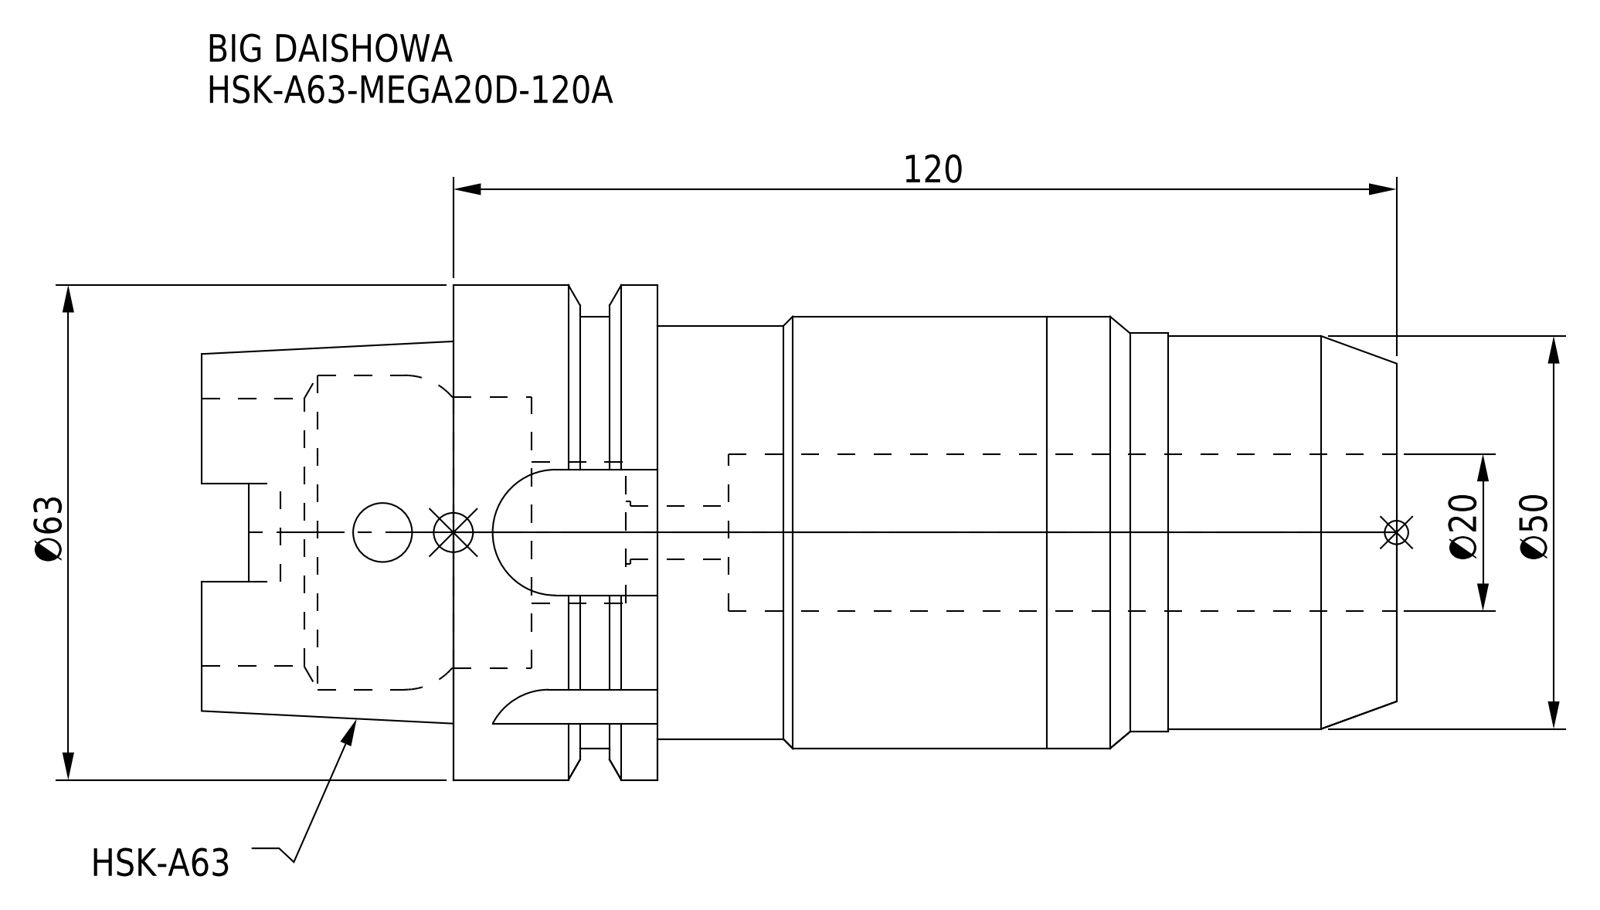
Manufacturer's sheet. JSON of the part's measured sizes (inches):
{"part_name": "HSK-A63-MEGA20D-120A", "step_written_by": "CREO PARAMETRIC BY PTC INC, 2016380 (AUTOMOTIVE_DESIGN)", "units": "inches", "bodies": {"solids": 1, "faces": 102, "planar": 39, "cylindrical": 43, "other": 20}, "overall_size": [5.984, 2.48, 2.48], "volume_in3": 15.74, "surface_area_in2": 66.61, "round_holes": [[0.266, 1], [0.295, 1], [0.315, 1], [0.709, 1], [0.787, 1], [1.339, 1], [1.358, 1], [1.575, 1]], "round_bosses_or_shafts": [[2.48, 1], [2.165, 1], [2.071, 1], [1.996, 1], [1.969, 1]], "partial_cylinders_radius": [[0.113, 4], [0.315, 4]], "face_to_face_distances": [4.724, 1.024, 3.701, 4.333, 0.632, 0.392, 5.984, 2.283, 1.652, 1.26]}
